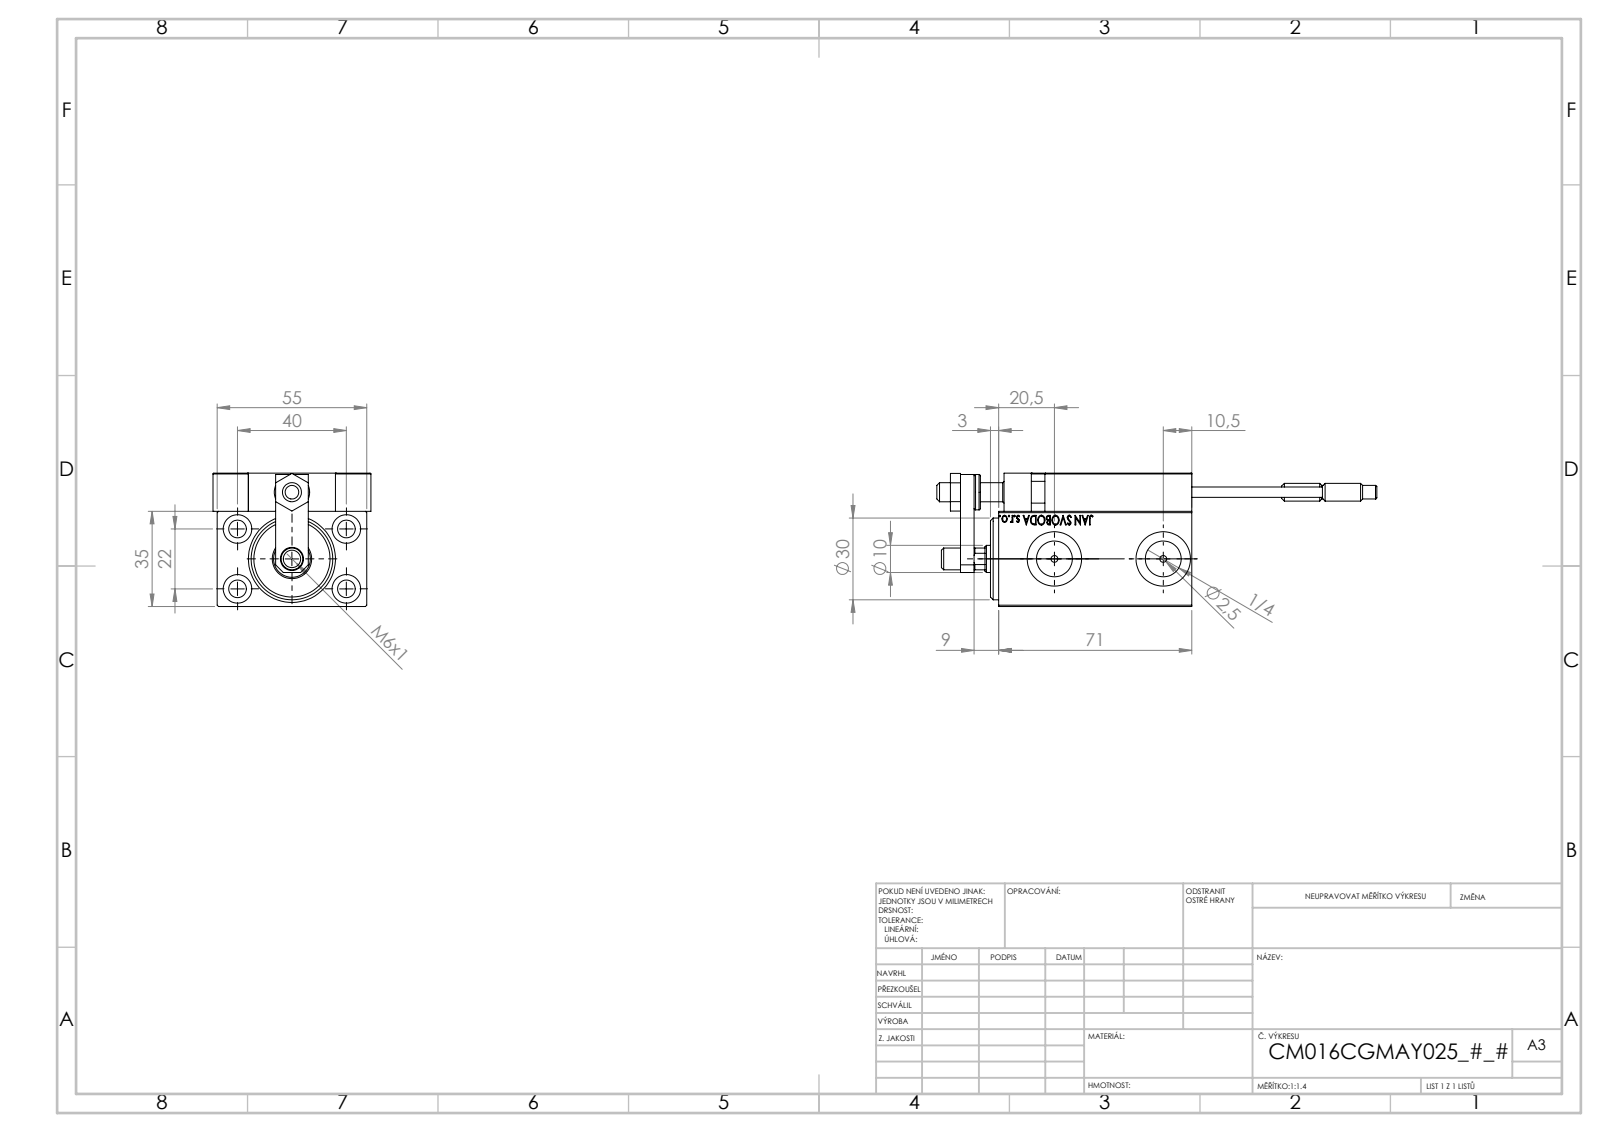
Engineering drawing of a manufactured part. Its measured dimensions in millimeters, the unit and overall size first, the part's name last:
Units: millimetres
Overall size (bounding box): 161.7 × 58 × 49
Round holes (diameter × count): ⌀8 ×5, ⌀3.2 ×4, ⌀4 ×4, ⌀6.5 ×4, ⌀10.5 ×4, ⌀2.5 ×2, ⌀5 ×2, ⌀13.16 ×2, ⌀20 ×2, ⌀4.5 ×1, ⌀7 ×1, ⌀8.5 ×1
Round bosses / shafts (diameter × count): ⌀5 ×4, ⌀6.5 ×2, ⌀3.8 ×2, ⌀13 ×1, ⌀11 ×1, ⌀8 ×1, ⌀6 ×1
Partial cylindrical surfaces — rounded edges, fillets, slot ends (radius × count): R0.3 ×30, R3 ×2, R4.5 ×1
Main face-to-face distances: 35, 5, 14, 49, 10, 7, 3, 55, 59, 1.5
Hole centre spacings: 22.83, 40, 11.37, 20, 22, 23.09, 24.13, 29.59
Volume: 163 429 mm³ · Surface area: 56 620 mm²
Bodies: 24 solids, 1321 faces (567 planar, 202 cylindrical, 552 other)
Part name (STEP PRODUCT): V450CM_C_Body; ALLEN BOLT D5; ZARAZKA; SWITCH X (+7 more)
STEP written by: SolidWorks 2019 (CONFIG_CONTROL_DESIGN)
